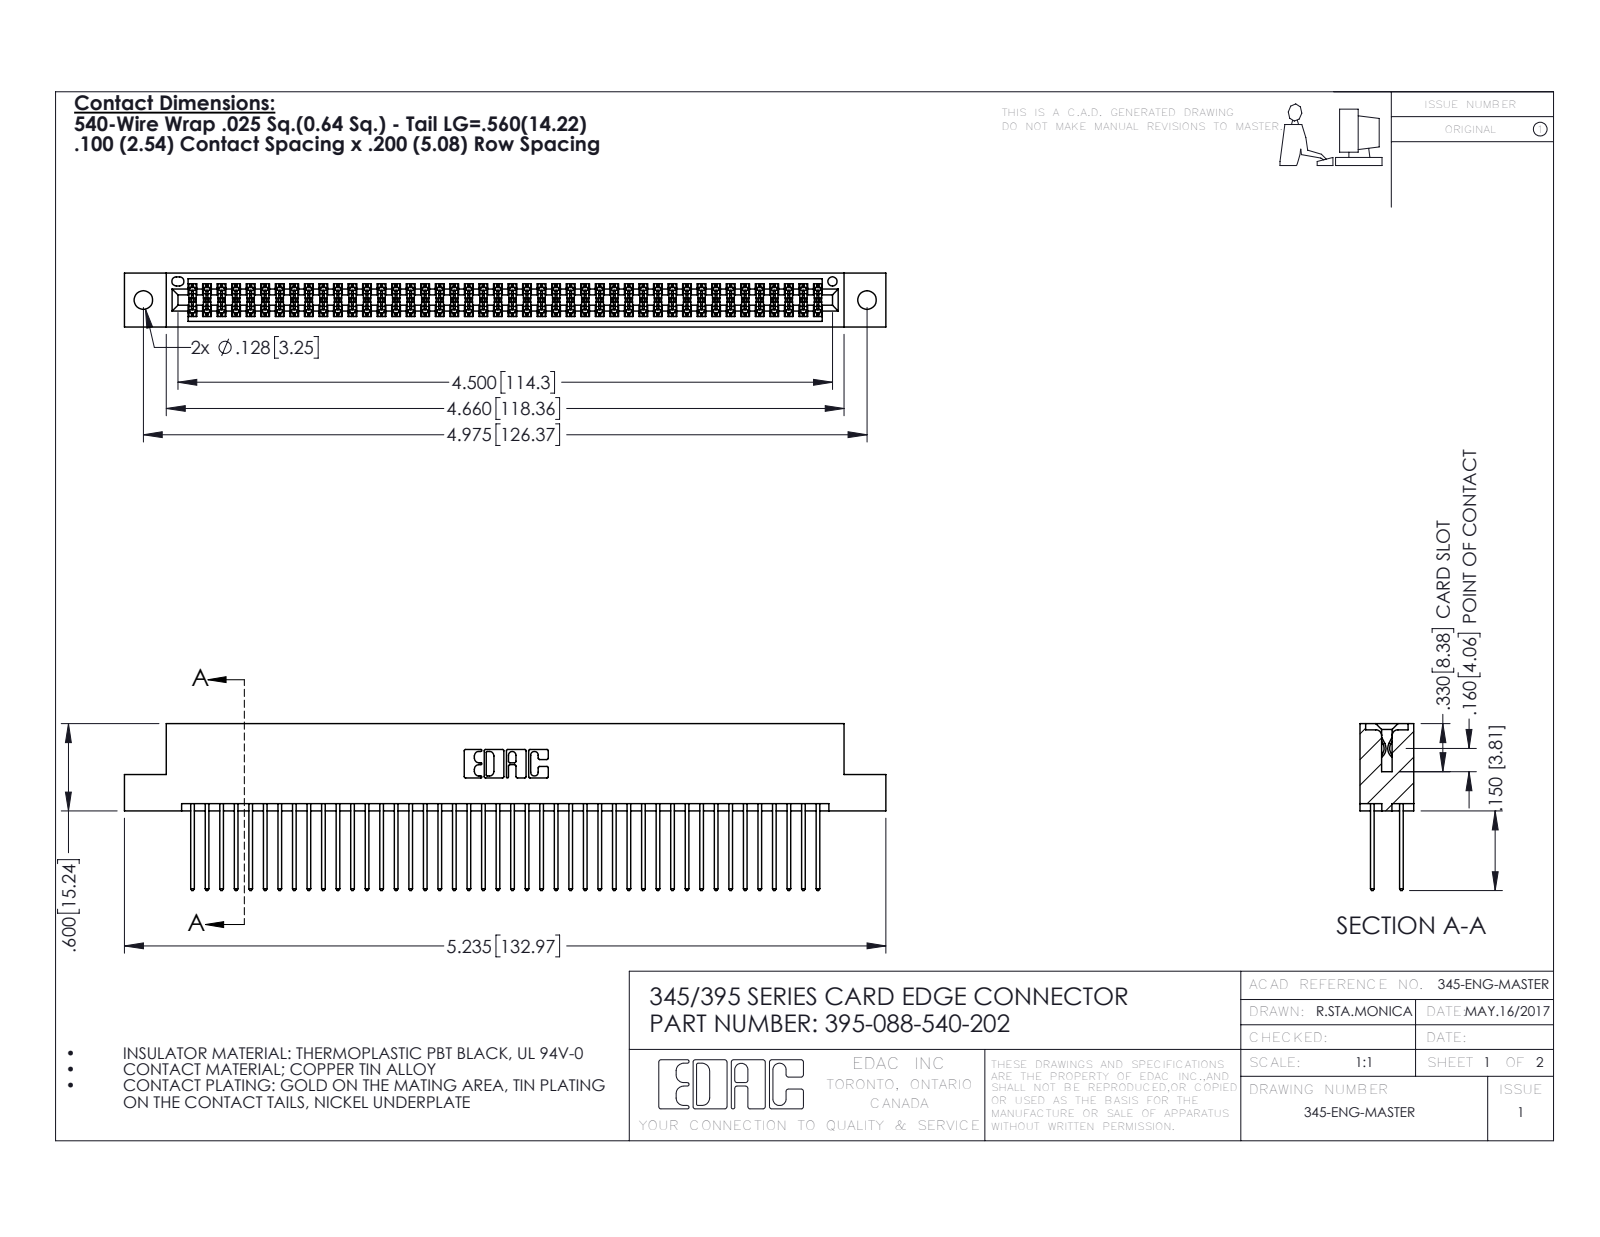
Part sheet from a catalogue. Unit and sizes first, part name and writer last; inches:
Units: inches
Overall size (bounding box): 5.235 × 1.147 × 0.37
Round holes (diameter × count): ⌀0.128 ×2, ⌀0.064 ×1
Partial cylindrical surfaces — rounded edges, fillets, slot ends (radius × count): R0.006 ×132, R0.01 ×88, R0.01 ×22, R0.007 ×6, R0.031 ×6, R0.026 ×3, R0.014 ×2, R0.019 ×2
Main face-to-face distances: 0.298, 0.072, 0.2, 0.098, 0.272, 0.025, 0.37, 0.225, 0.175, 0.149
Hole centre spacings: 0.27, 4.739, 4.975
Volume: 0.807 in³ · Surface area: 32.35 in²
Bodies: 89 solids, 4526 faces (2984 planar, 1542 cylindrical, 0 other)
Part name (STEP PRODUCT): 345-292-001_345-293-140; 345 Part_Flush Mounting Lugs - 0.128 Dia; 395-088-540-202
STEP written by: SolidWorks 2016 (CONFIG_CONTROL_DESIGN)
